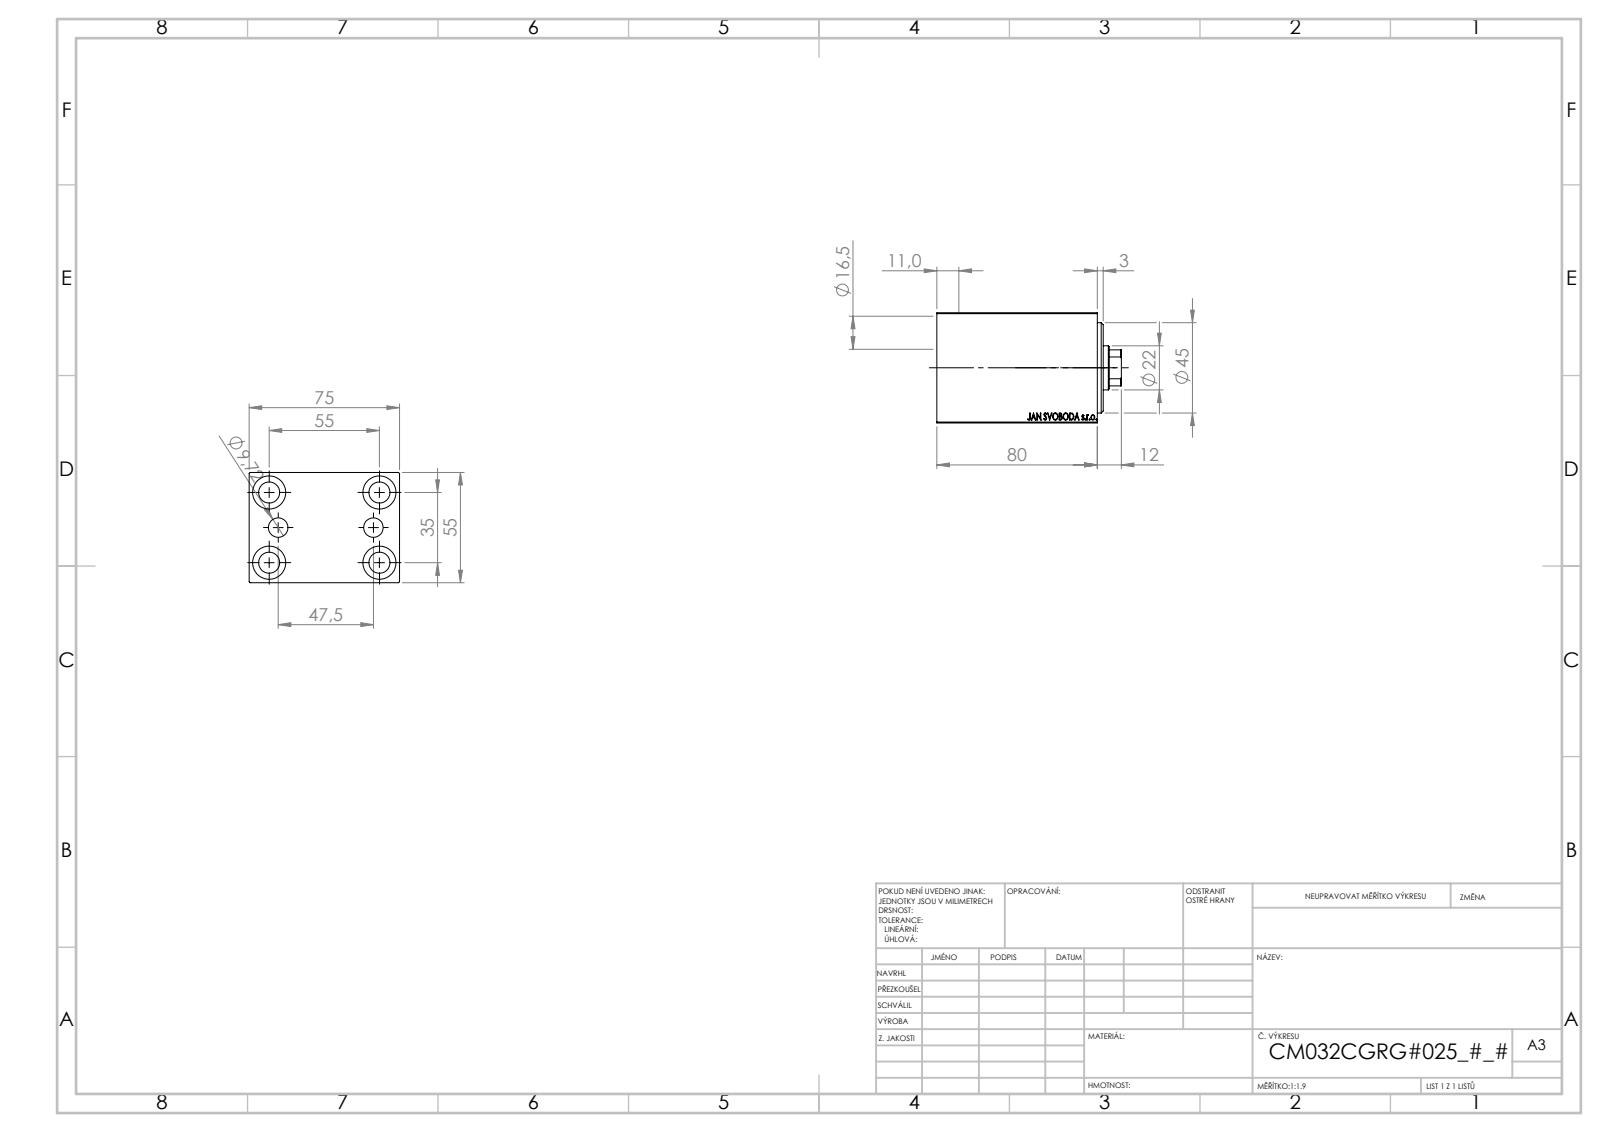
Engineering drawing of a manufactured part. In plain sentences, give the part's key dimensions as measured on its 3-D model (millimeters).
The part is named "V450CM_C_VCP; V450CM_VC_B; V450CM_C_Body". Its 3-D file was written by "SolidWorks 2019 (CONFIG_CONTROL_DESIGN)". It is 3 solids with 858 faces: 408 planar, 56 cylindrical and 394 other. Overall it measures 92 by 75 by 55 millimeters. Its volume is 283 127 cubic millimeters and its surface area 60 344 square millimeters. Round holes: 5 of diameter 10.5, 4 of diameter 16.5, 2 of diameter 4, 2 of diameter 9.72, 1 of diameter 22, 1 of diameter 25.5, 1 of diameter 32, 1 of diameter 34, 1 of diameter 45. Partial cylindrical surfaces (rounded edges, fillets, slot ends): 1 of radius 10.5. The main face-to-face distances are 55, 75, 5, 27.5, 52.5, 80, 47.5, 11, 69, 3. The hole center spacings are 17.9, 32.6, 54.16, 23.75, 35, 55, 65.19, 47.5.
